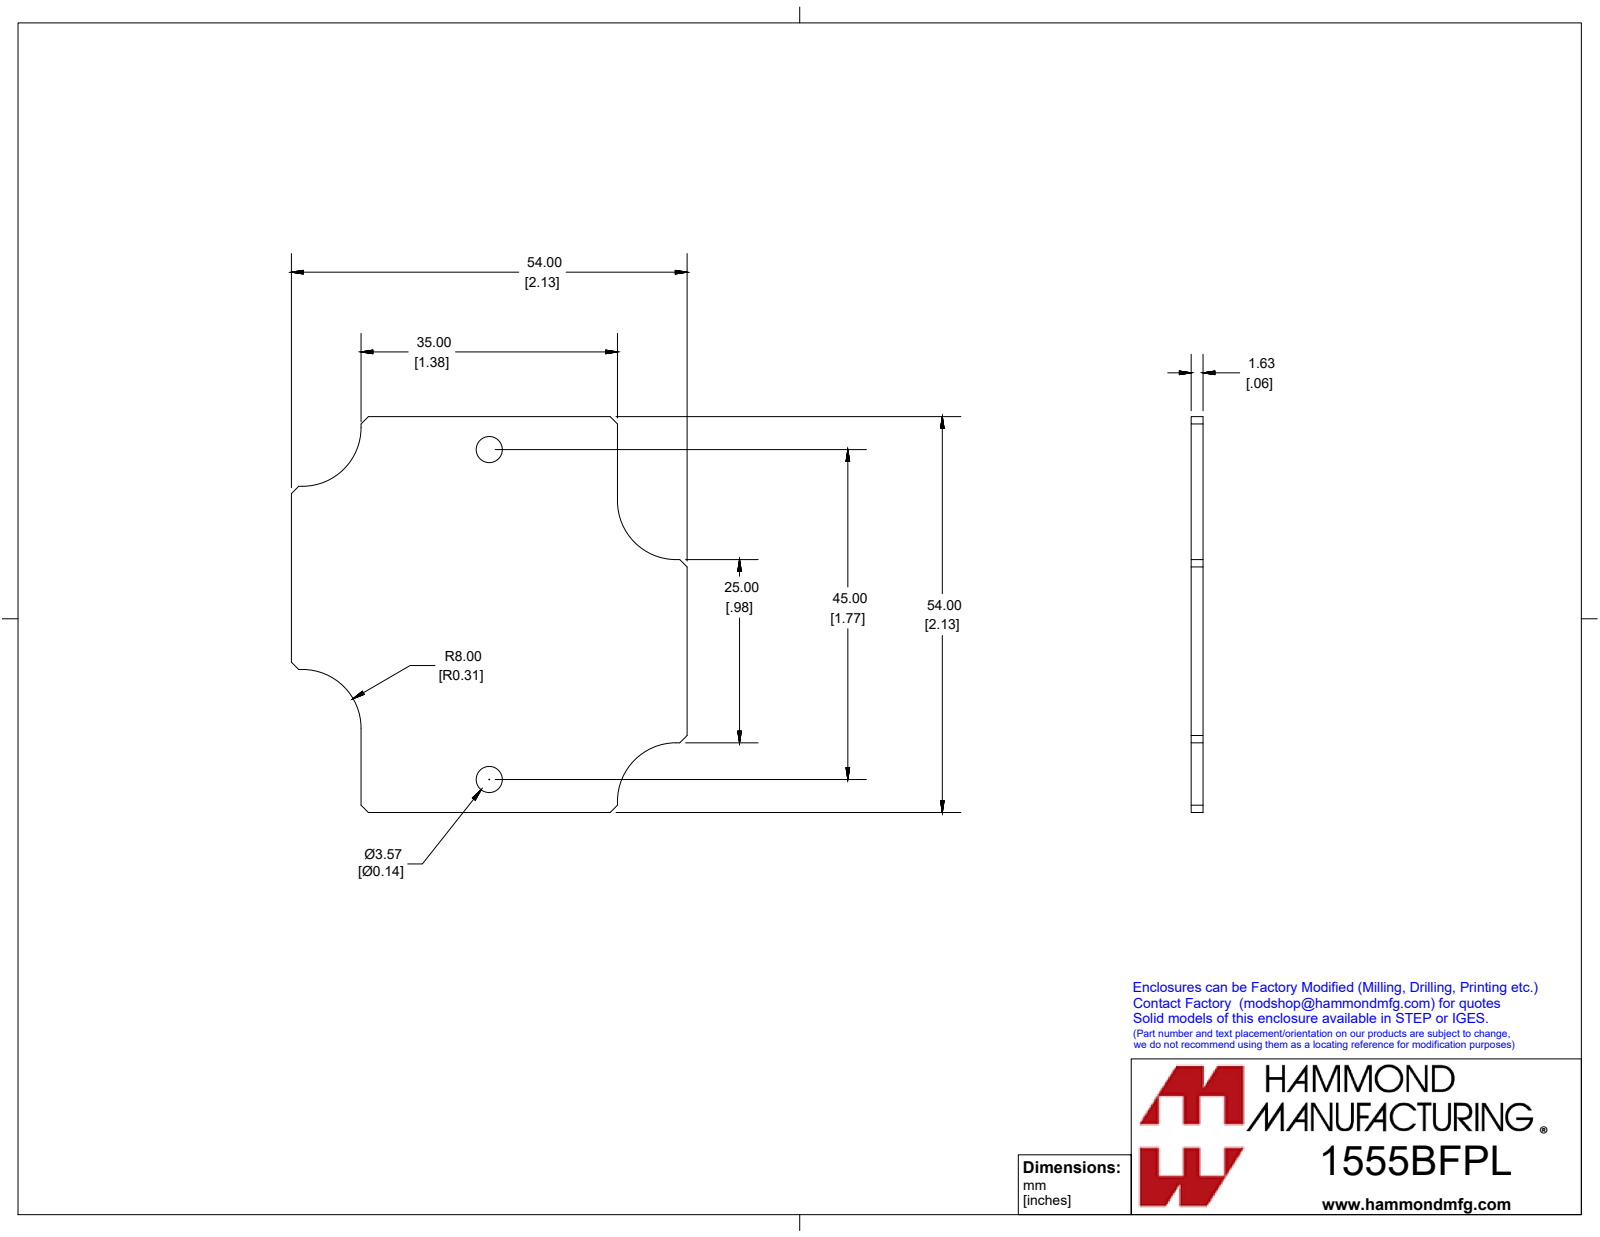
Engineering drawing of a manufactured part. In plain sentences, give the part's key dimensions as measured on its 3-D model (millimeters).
The part is named "1555BFPL". Its 3-D file was written by "SolidWorks 2019 (CONFIG_CONTROL_DESIGN)". It is 1 solid with 28 faces: 22 planar, 6 cylindrical and 0 other. Overall it measures 54 by 54 by 1.6 millimeters. Its volume is 3 880 cubic millimeters and its surface area 5 147 square millimeters. Round holes: 2 of diameter 3.7. Partial cylindrical surfaces (rounded edges, fillets, slot ends): 4 of radius 8. The main face-to-face distances are 1.6, 54, 9.5, 44.5, 35, 61.5, 7.1, 54.4, 47.4, 19.5. The hole center spacings are 45.
